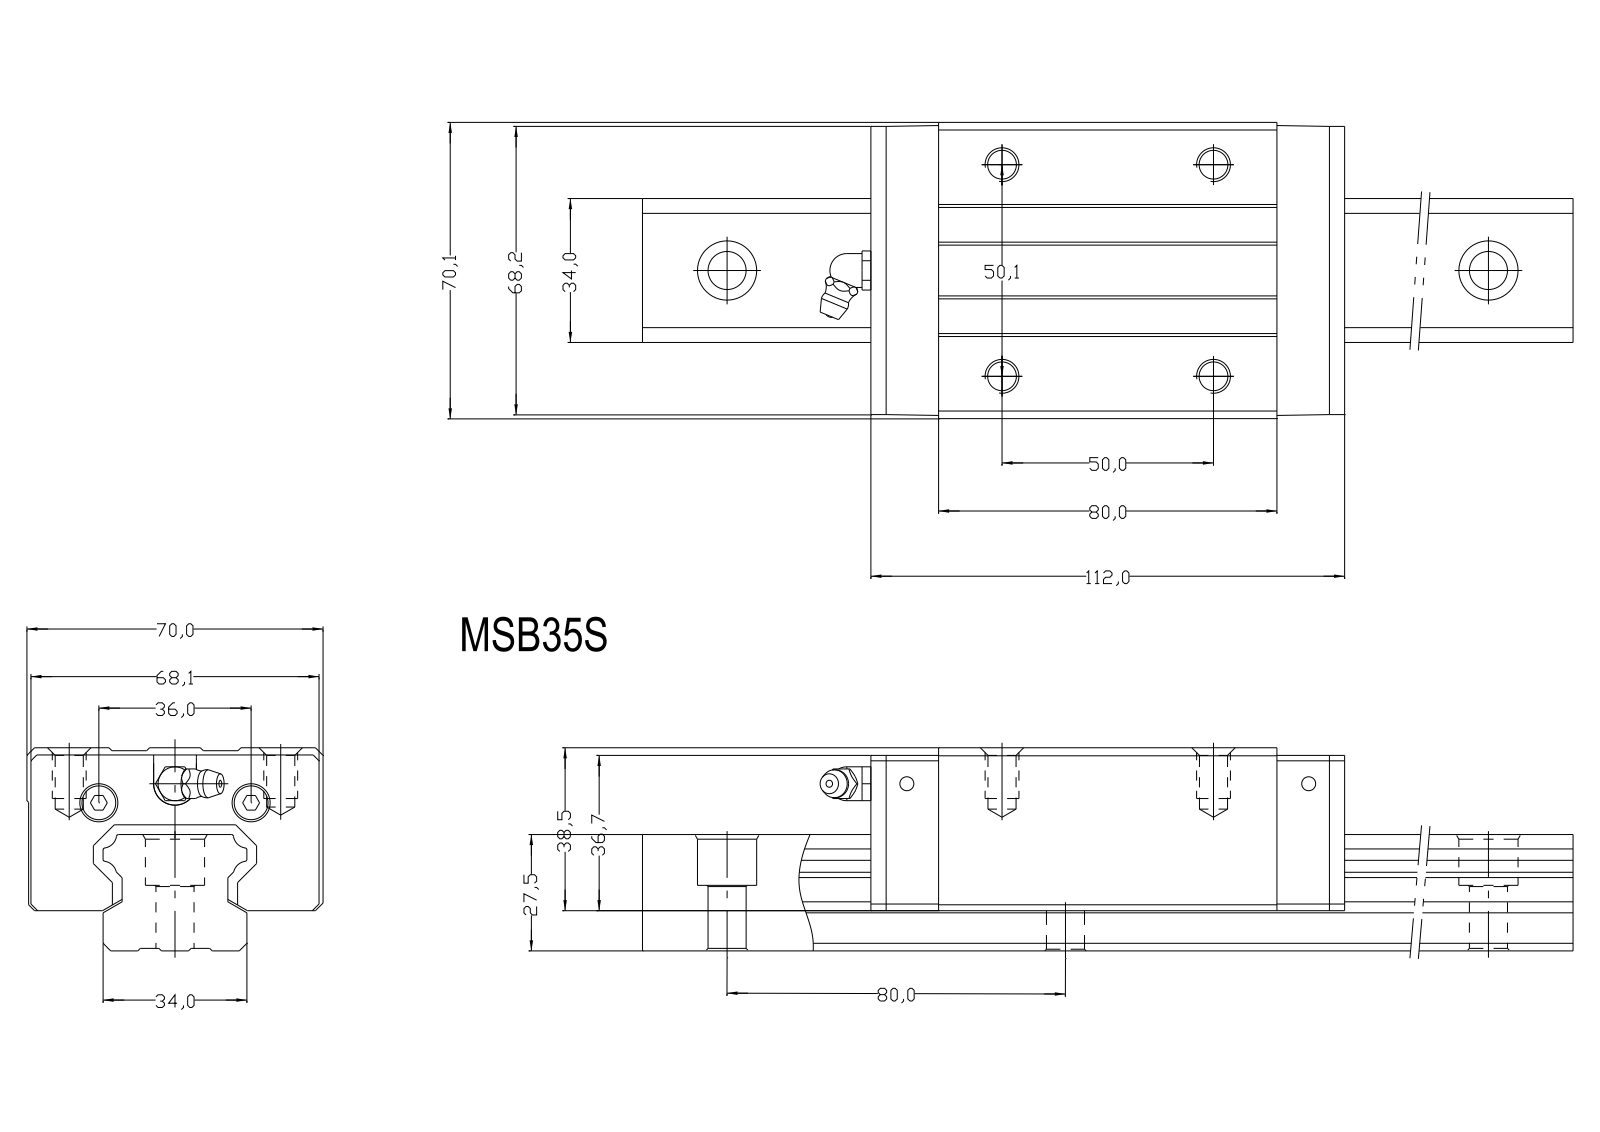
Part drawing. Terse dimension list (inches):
written by: Kubotek KeyCreator V6.5.2 (0407) (CONFIG_CONTROL_DESIGN)
unit: in
bodies: 3 solids, 224 faces (133 planar, 74 cylindrical, 17 other)
size: 11.024 × 2.756 × 1.89
volume: 27.51 in³; area: 118.3 in²
holes: 6× ⌀0.354, 4× ⌀0.13, 4× ⌀0.315, 4× ⌀0.551
bosses: 1× ⌀0.315
rounds: 6× R0.02, 4× R0.138, 1× R0.201
face distances: 0.709, 1.083, 1.161, 0.177, 0.807, 1.89, 0.374, 1.516, 0.886, 1.87
hole spacings: 1.148, 1.969, 2.742, 3.867, 5.793, 3.15, 2.784, 6.299
